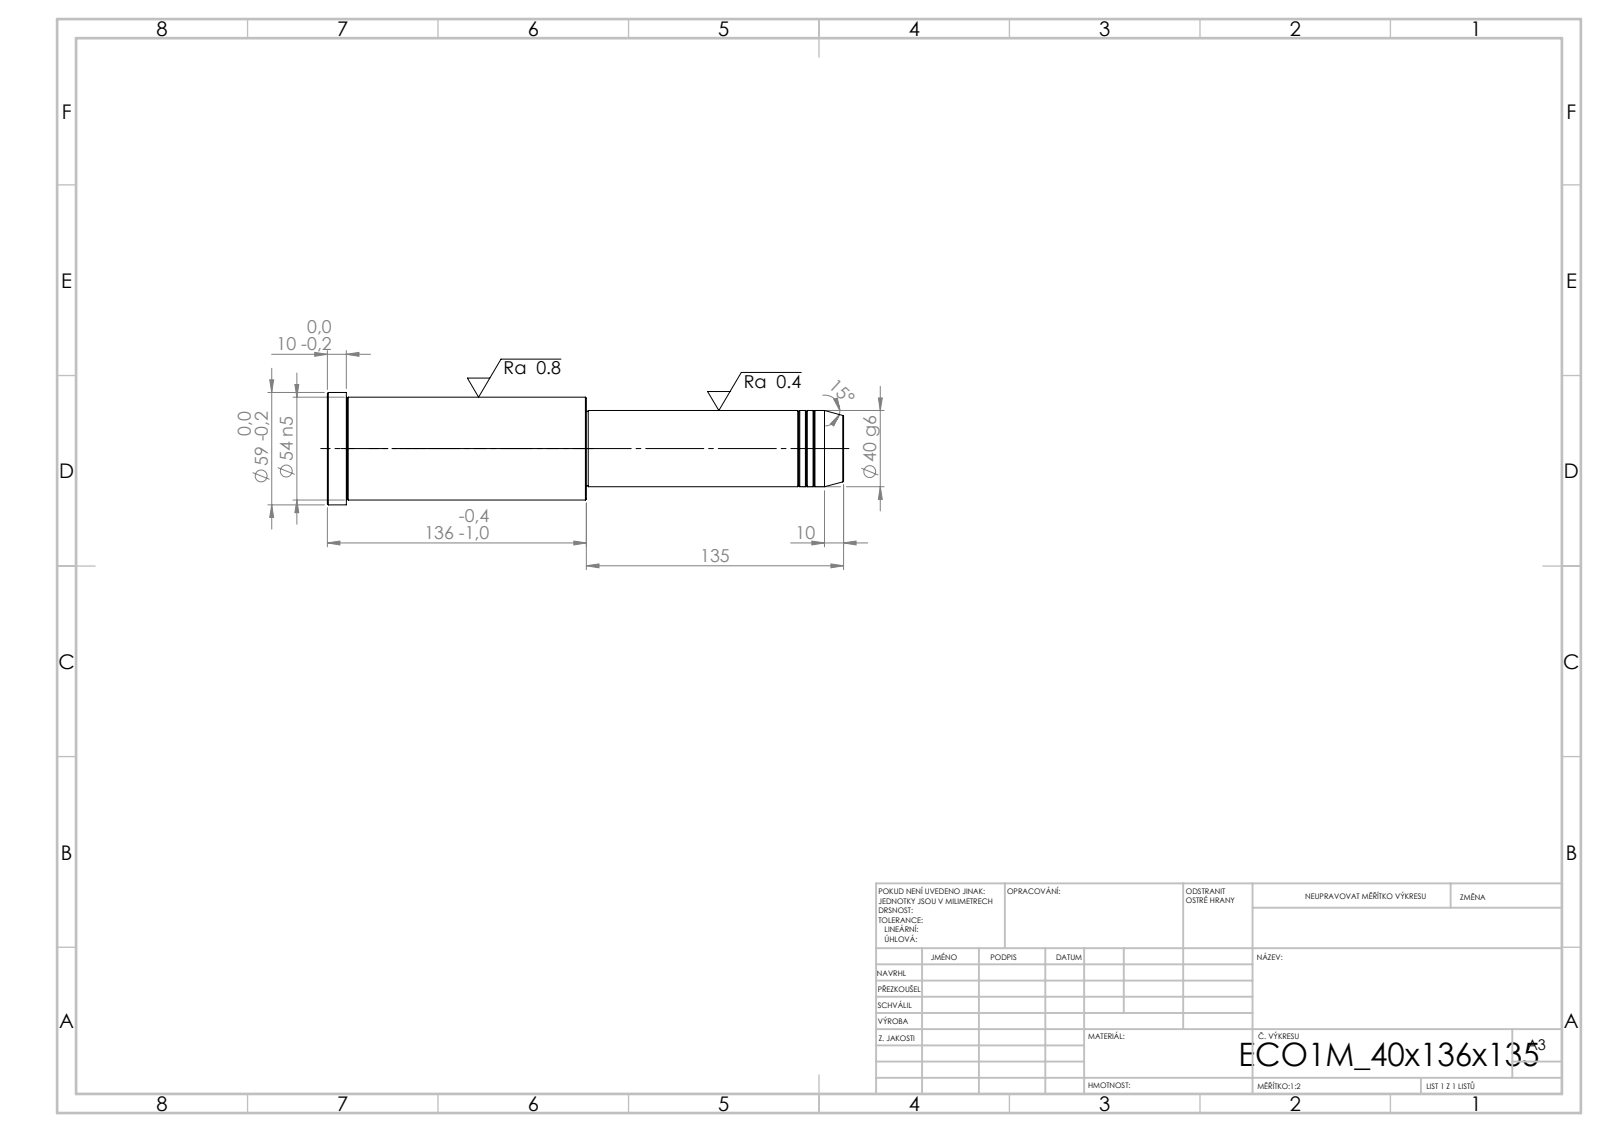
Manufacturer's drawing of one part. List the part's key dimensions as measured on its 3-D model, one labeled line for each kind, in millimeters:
STEP written by: SolidWorks 2019 (CONFIG_CONTROL_DESIGN)
Units: millimetres
Bodies: 1 solid, 43 faces (5 planar, 14 cylindrical, 24 other)
Overall size (bounding box): 271 × 59 × 59
Volume: 483 623 mm³ · Surface area: 45 608 mm²
Round bosses / shafts (diameter × count): ⌀59 ×1, ⌀54 ×1, ⌀40 ×1, ⌀39 ×1
Main face-to-face distances: 136, 135, 271, 261, 126, 10, 134, 1, 127, 137
